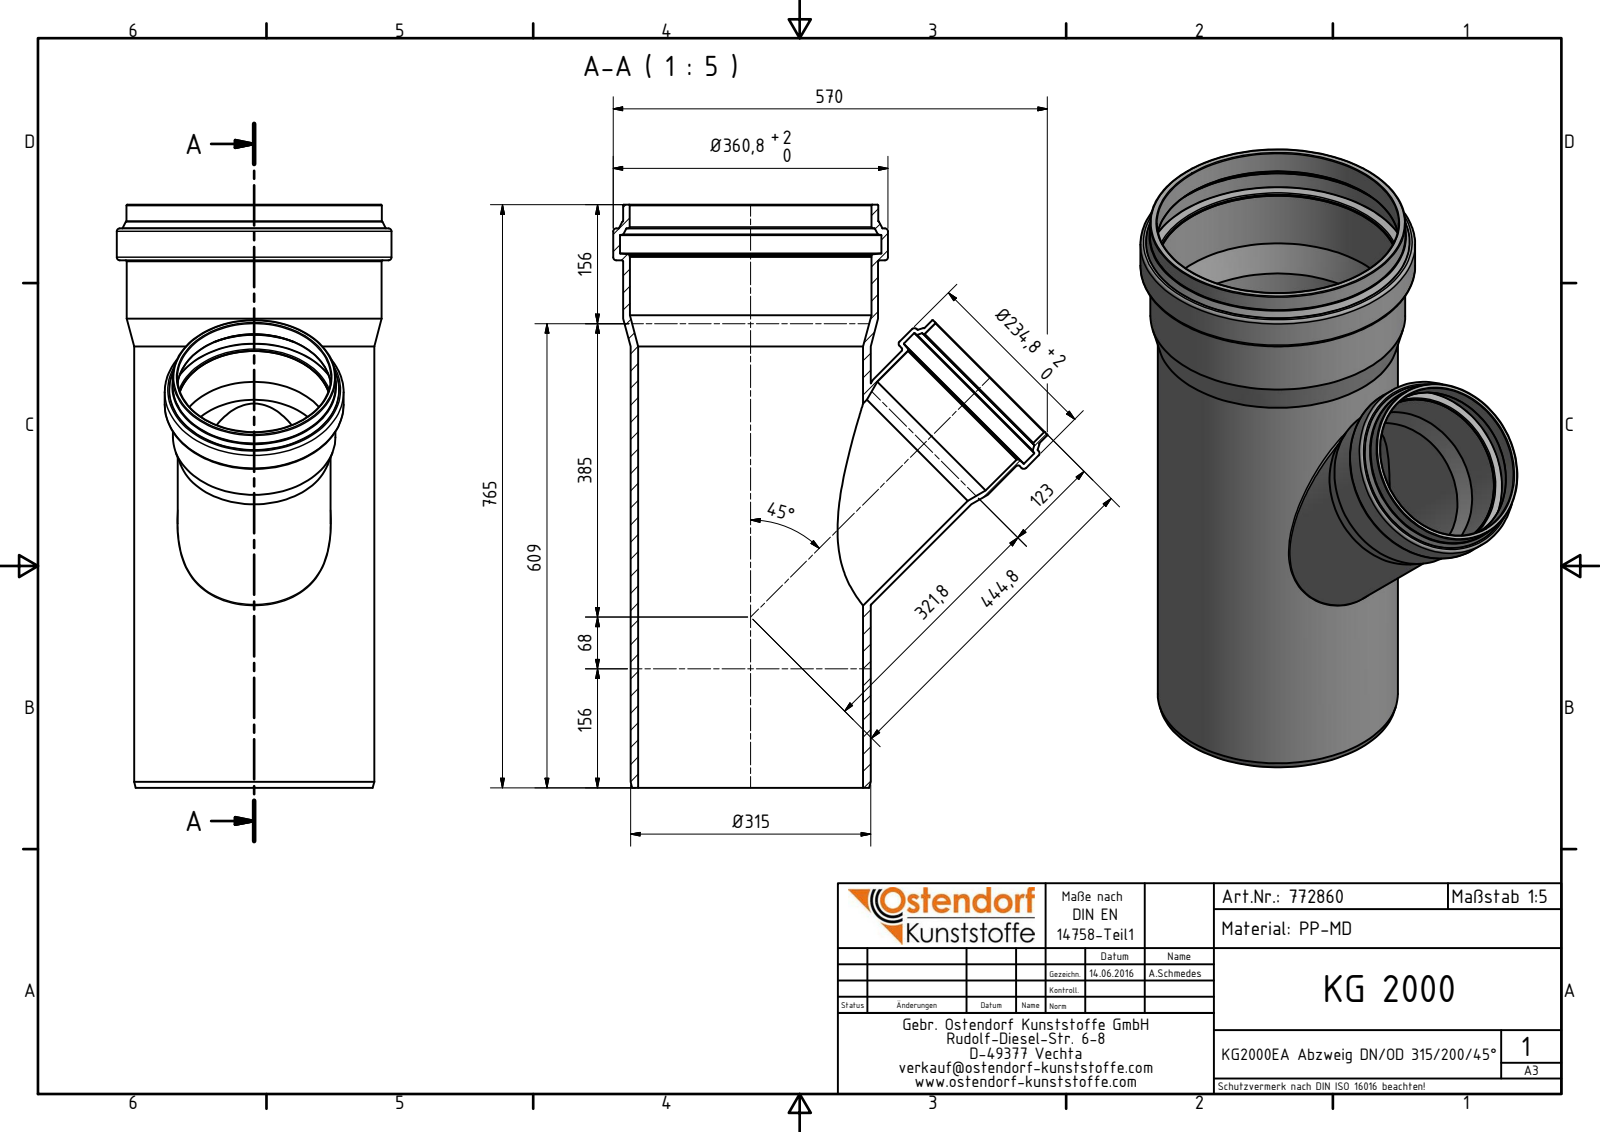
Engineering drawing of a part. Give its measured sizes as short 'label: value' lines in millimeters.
name: 772860 KG2000EA Abzweig DN_OD 315_200_45°
written by: Autodesk Inventor 2016 (AUTOMOTIVE_DESIGN)
unit: mm
bodies: 1 solid, 71 faces (9 planar, 18 cylindrical, 44 other)
size: 765 × 570 × 360.8
volume: 8 099 000 mm³; area: 1 809 000 mm²
holes: 2× ⌀201.8, 1× ⌀187.4, 1× ⌀201.5, 1× ⌀223, 1× ⌀295.3, 1× ⌀317.1, 1× ⌀317.5, 1× ⌀343.2
bosses: 1× ⌀360.8, 1× ⌀335.1, 1× ⌀334.7, 1× ⌀315.3, 1× ⌀234.8, 1× ⌀213.6, 1× ⌀213.3, 1× ⌀200.4
face distances: 692.1, 765, 72.9, 734.1, 42, 30.9, 54.89, 31.6, 23.29, 696.43
